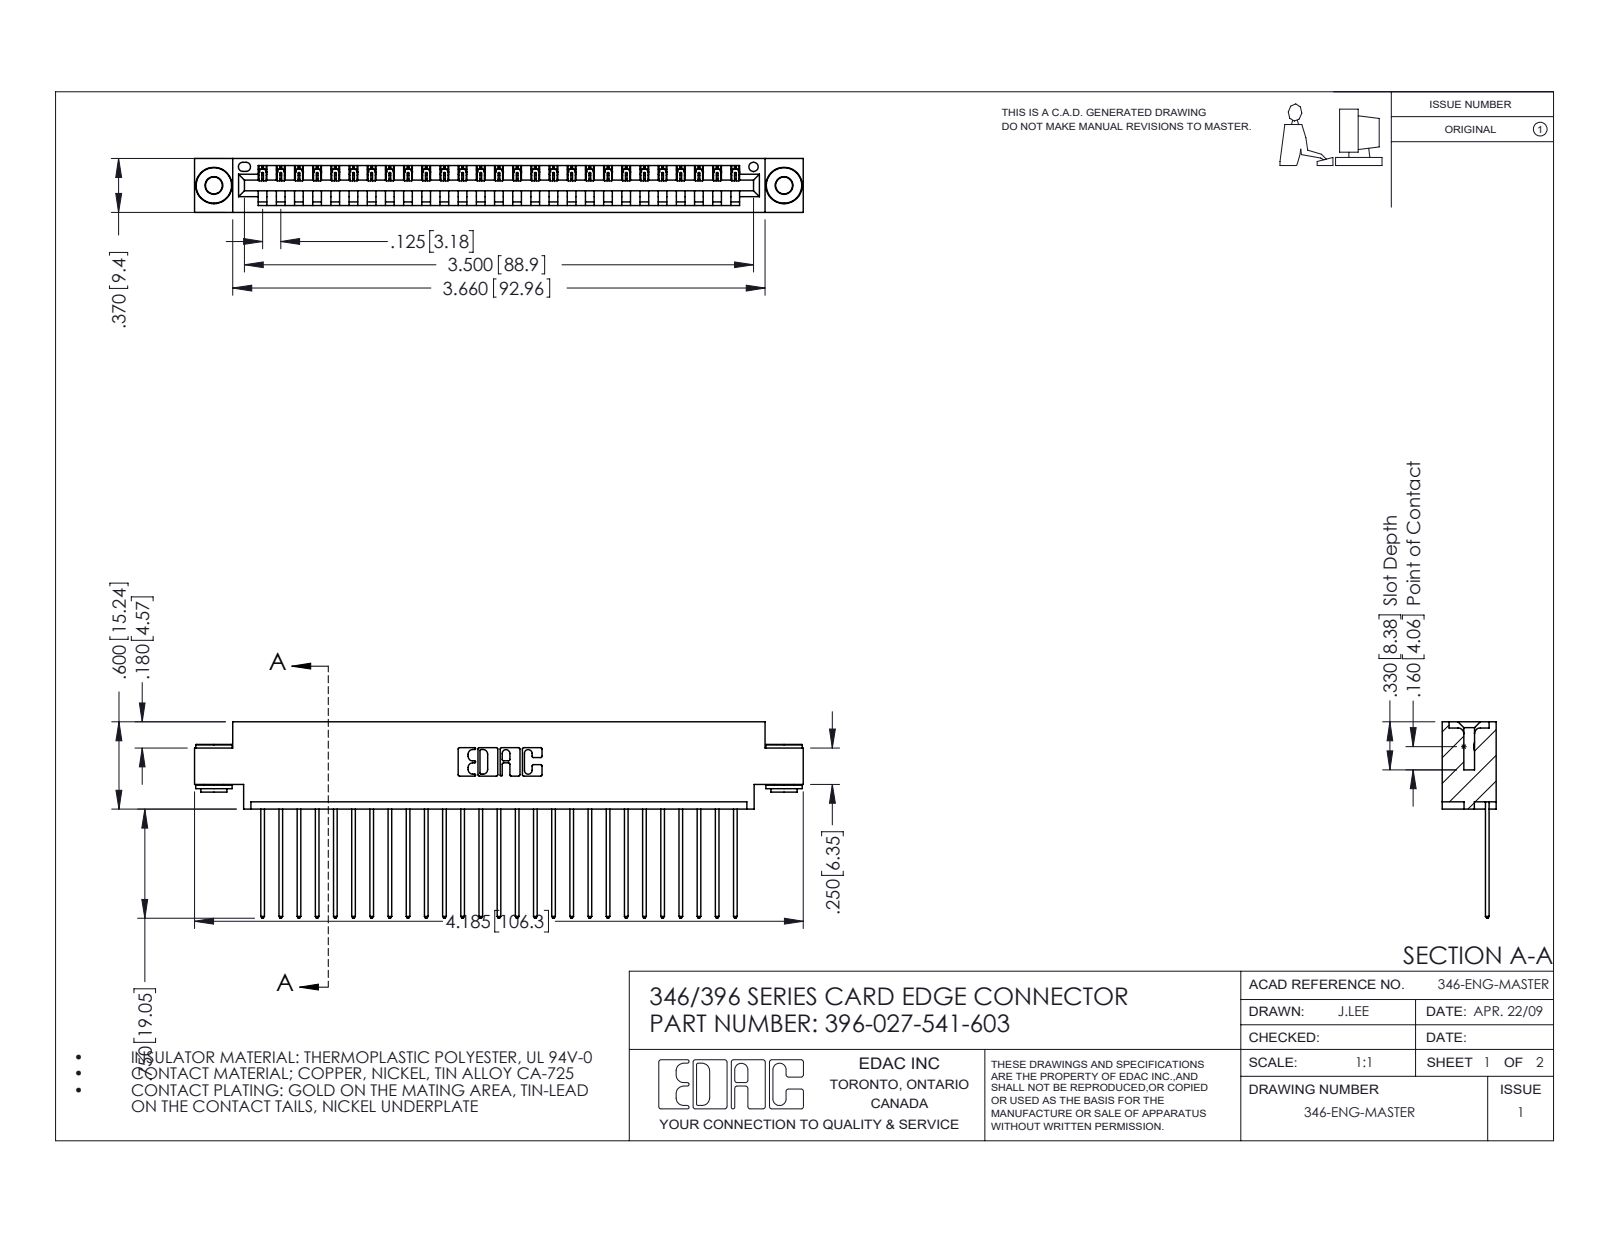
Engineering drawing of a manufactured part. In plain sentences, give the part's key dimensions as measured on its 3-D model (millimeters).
The part is named "396-027-541-603; 345-250-002_345-250-002-102; 345-292-001_345-293-141; 346 Part_0.170 Offset - 0.156 Dia-TH". Its 3-D file was written by "SolidWorks 2016 (CONFIG_CONTROL_DESIGN)". It is 30 solids with 1730 faces: 1170 planar, 552 cylindrical and 8 other. Overall it measures 106.3 by 34.3 by 9.4 millimeters. Its volume is 10 000 cubic millimeters and its surface area 13 280 square millimeters. Round holes: 2 of diameter 2.9, 2 of diameter 4, 1 of diameter 1.6. Round bosses or shafts: 2 of diameter 6.4, 2 of diameter 4.6, 2 of diameter 3.5. Partial cylindrical surfaces (rounded edges, fillets, slot ends): 54 of radius 0.2, 54 of radius 0.3, 22 of radius 0.3, 6 of radius 0.2, 6 of radius 0.8, 3 of radius 0.7, 2 of radius 0.8, 2 of radius 1. The main face-to-face distances are 1.2, 8.2, 9.4, 6.4, 0.6, 1.8, 7.6, 3.8, 5.6, 2.5. The hole center spacings are 6.2, 94.3, 99.6.
